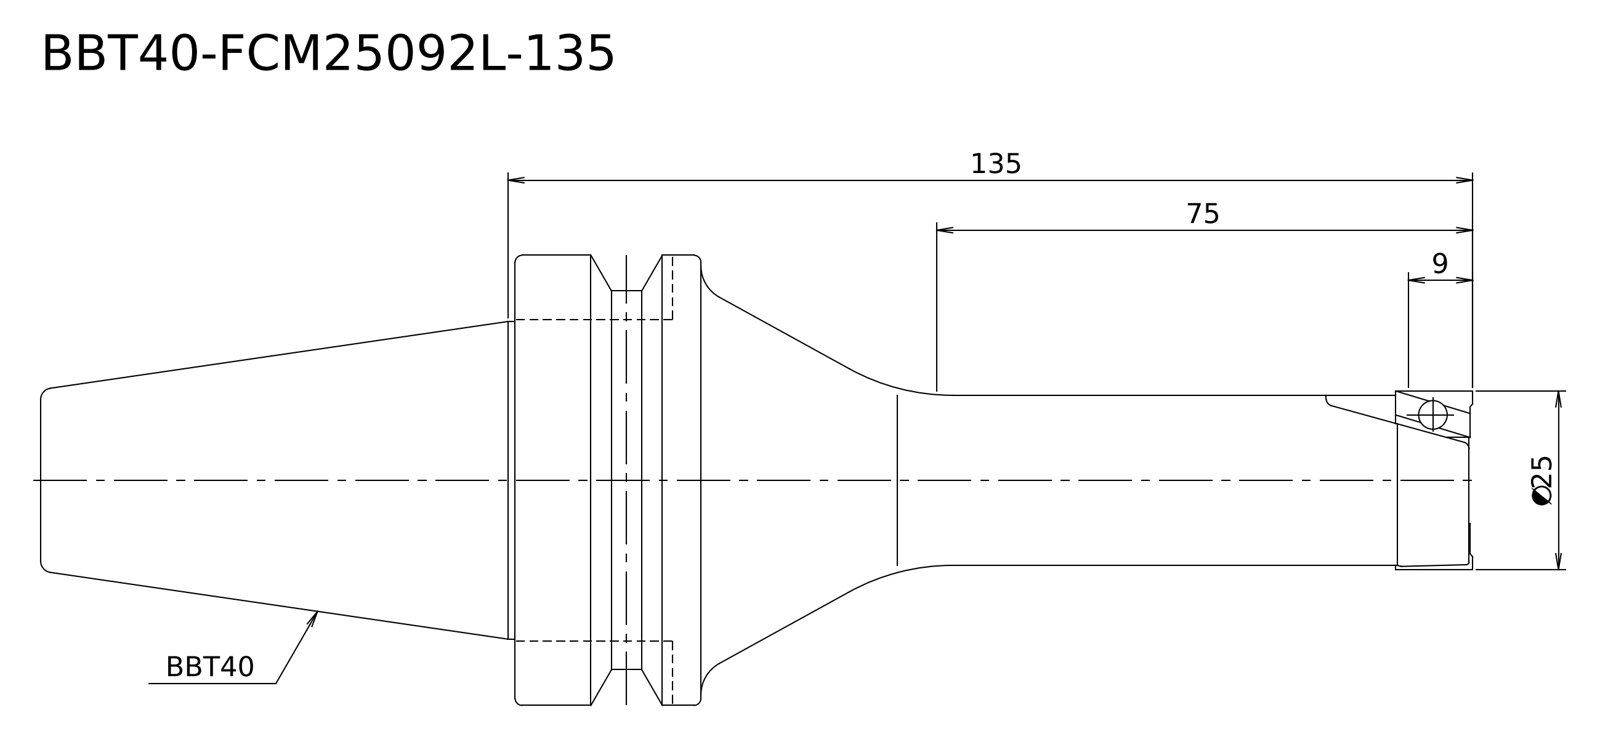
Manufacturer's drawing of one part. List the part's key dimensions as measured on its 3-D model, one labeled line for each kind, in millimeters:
STEP written by: Kubotek KeyCreator V8.5.1 (14335) (CONFIG_CONTROL_DESIGN)
Units: millimetres
Bodies: 1 solid, 17 faces (4 planar, 6 cylindrical, 7 other)
Overall size (bounding box): 200.4 × 63 × 63
Volume: 212 730 mm³ · Surface area: 26 569 mm²
Round bosses / shafts (diameter × count): ⌀63 ×1, ⌀53 ×1, ⌀44.45 ×1, ⌀25 ×1, ⌀23.8 ×1
Main face-to-face distances: 66.4, 134, 200.4, 108, 26, 92.4
